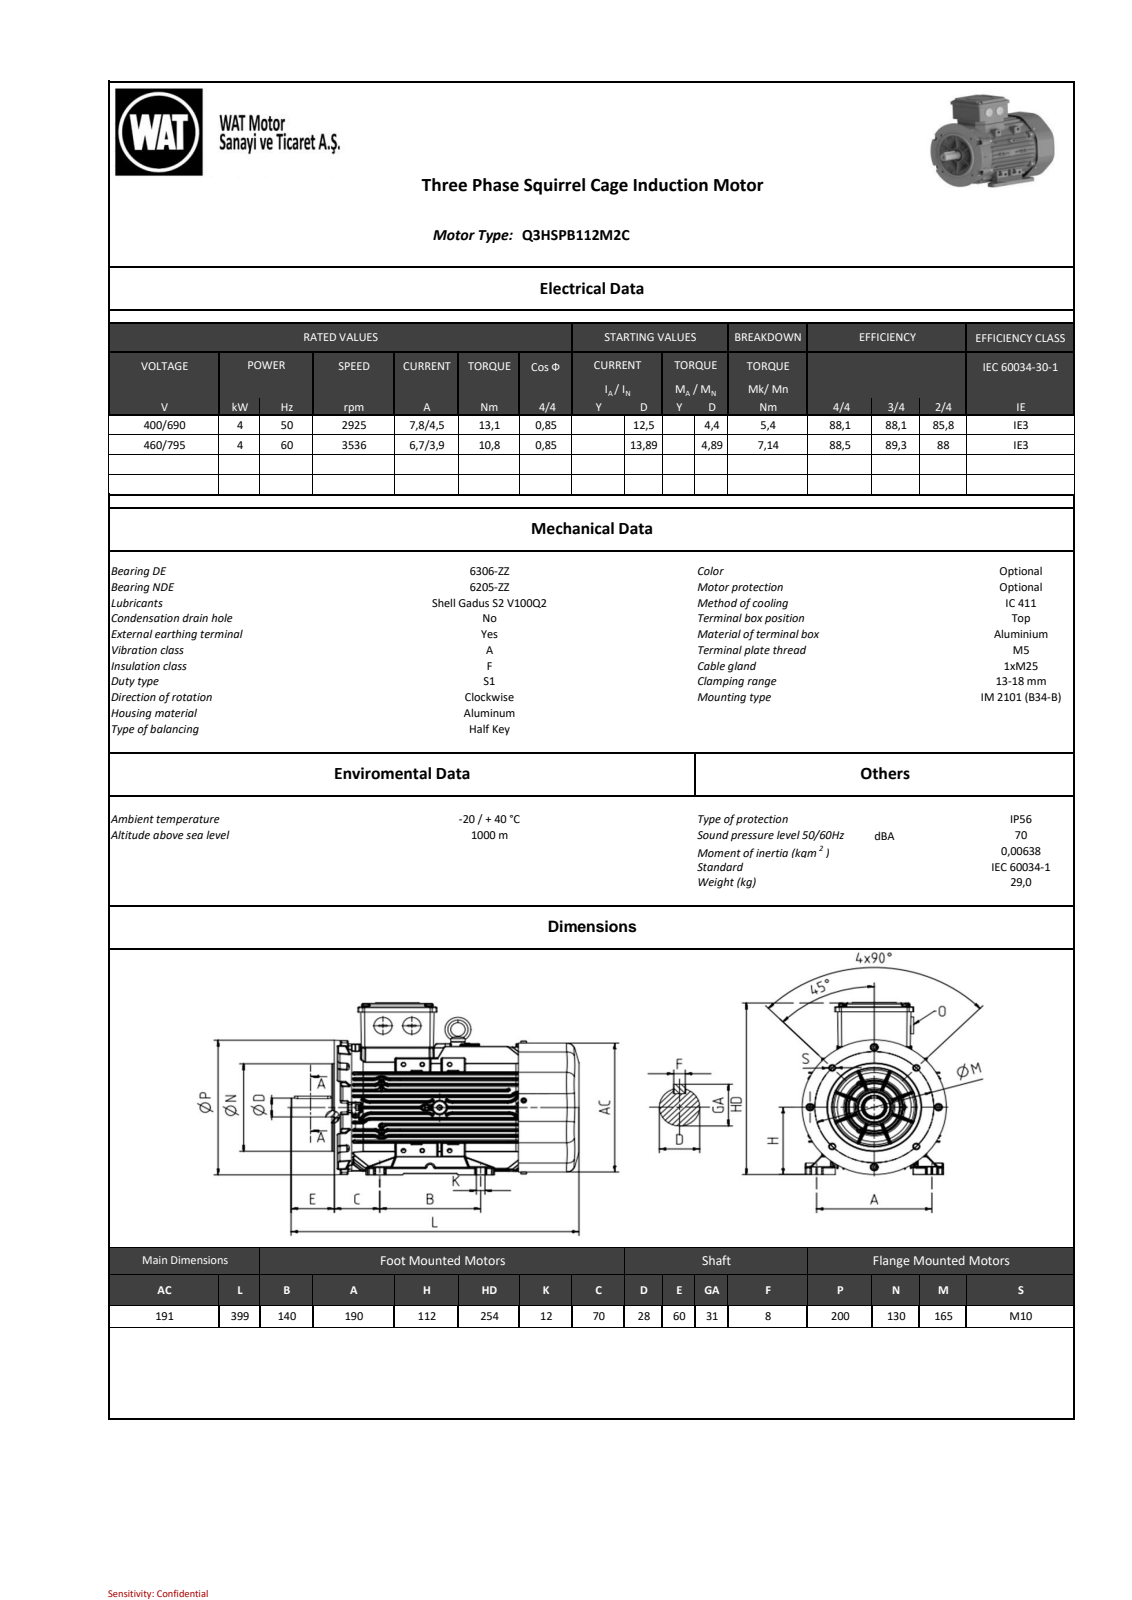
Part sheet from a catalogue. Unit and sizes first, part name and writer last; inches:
Units: inches
Overall size (bounding box): 15.721 × 10.048 × 8.737
Round holes (diameter × count): ⌀0.335 ×4, ⌀0.394 ×1, ⌀1.749 ×1, ⌀2.26 ×1, ⌀3.504 ×1, ⌀4.291 ×1, ⌀5.079 ×1, ⌀5.236 ×1
Round bosses / shafts (diameter × count): ⌀0.315 ×8, ⌀0.197 ×4, ⌀0.984 ×3, ⌀5.118 ×1, ⌀4.469 ×1, ⌀3.681 ×1, ⌀2.391 ×1, ⌀1.181 ×1
Partial cylindrical surfaces — rounded edges, fillets, slot ends (radius × count): R0.039 ×800, R0.031 ×620, R0.03 ×108, R0.079 ×81, R0.02 ×77, R0.032 ×50, R0.197 ×44, R0.591 ×26
Main face-to-face distances: 0.336, 0.333, 0.333, 3.002, 0.666, 3.679, 3.019, 1.007, 0.671, 2.348
Hole centre spacings: 3.248, 4.594, 6.496
Bodies: 0 solids, 6841 faces (1548 planar, 2770 cylindrical, 2523 other)
Part name (STEP PRODUCT): QHS Series_ 112_B34b_stp_objects
STEP written by: SIEMENS PLM Software NX2206.8101 (AUTOMOTIVE_DESIGN)
